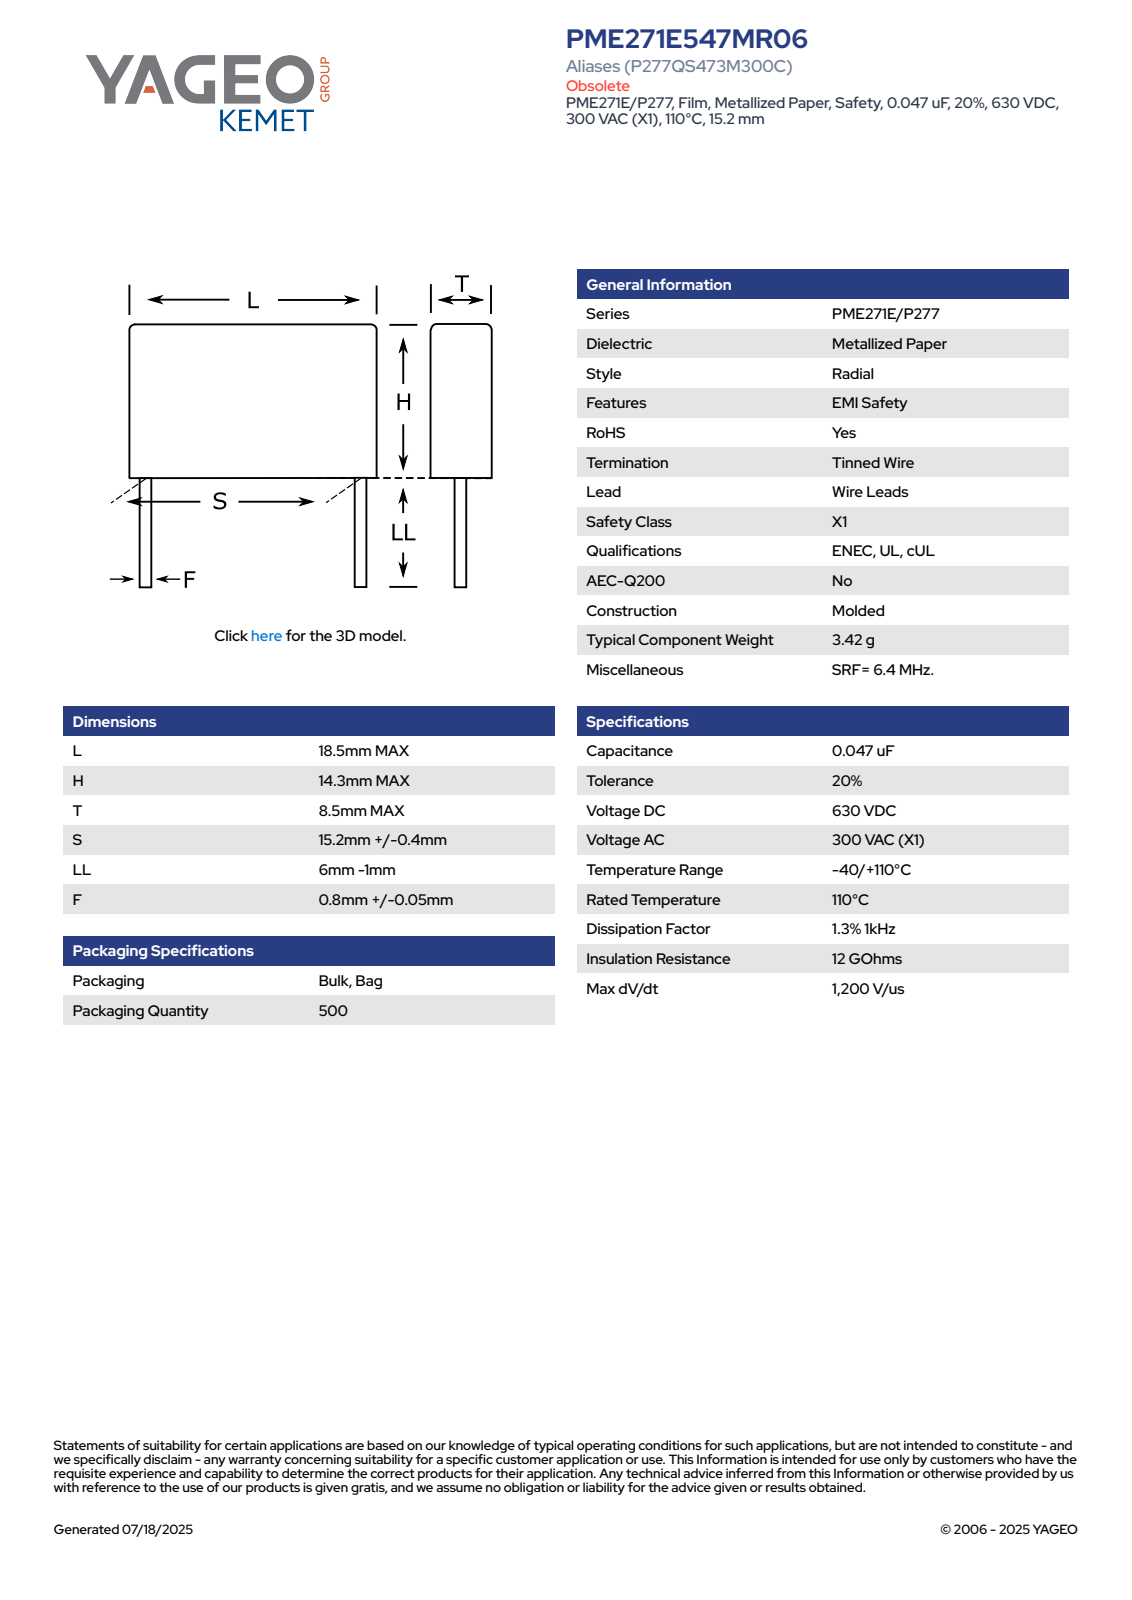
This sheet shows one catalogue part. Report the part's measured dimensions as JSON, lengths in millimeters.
{"part_name": "CFR_MOLDED_18.5X14.3X8.5_L18.5H14.3T8.5S15.2LL5F0.85", "step_written_by": "SolidWorks 2014 (AUTOMOTIVE_DESIGN)", "units": "millimeters", "bodies": {"solids": 4, "faces": 73, "planar": 65, "cylindrical": 8, "other": 0}, "overall_size": [19.3, 18.5, 8.51], "volume_mm3": 2252, "surface_area_mm2": 1118, "round_bosses_or_shafts": [[0.85, 2]], "partial_cylinders_radius": [[0.5, 4]], "face_to_face_distances": [8.5, 14.3, 18.5, 8.51, 5, 19.3, 12.65, 7.65, 6.65, 11]}
